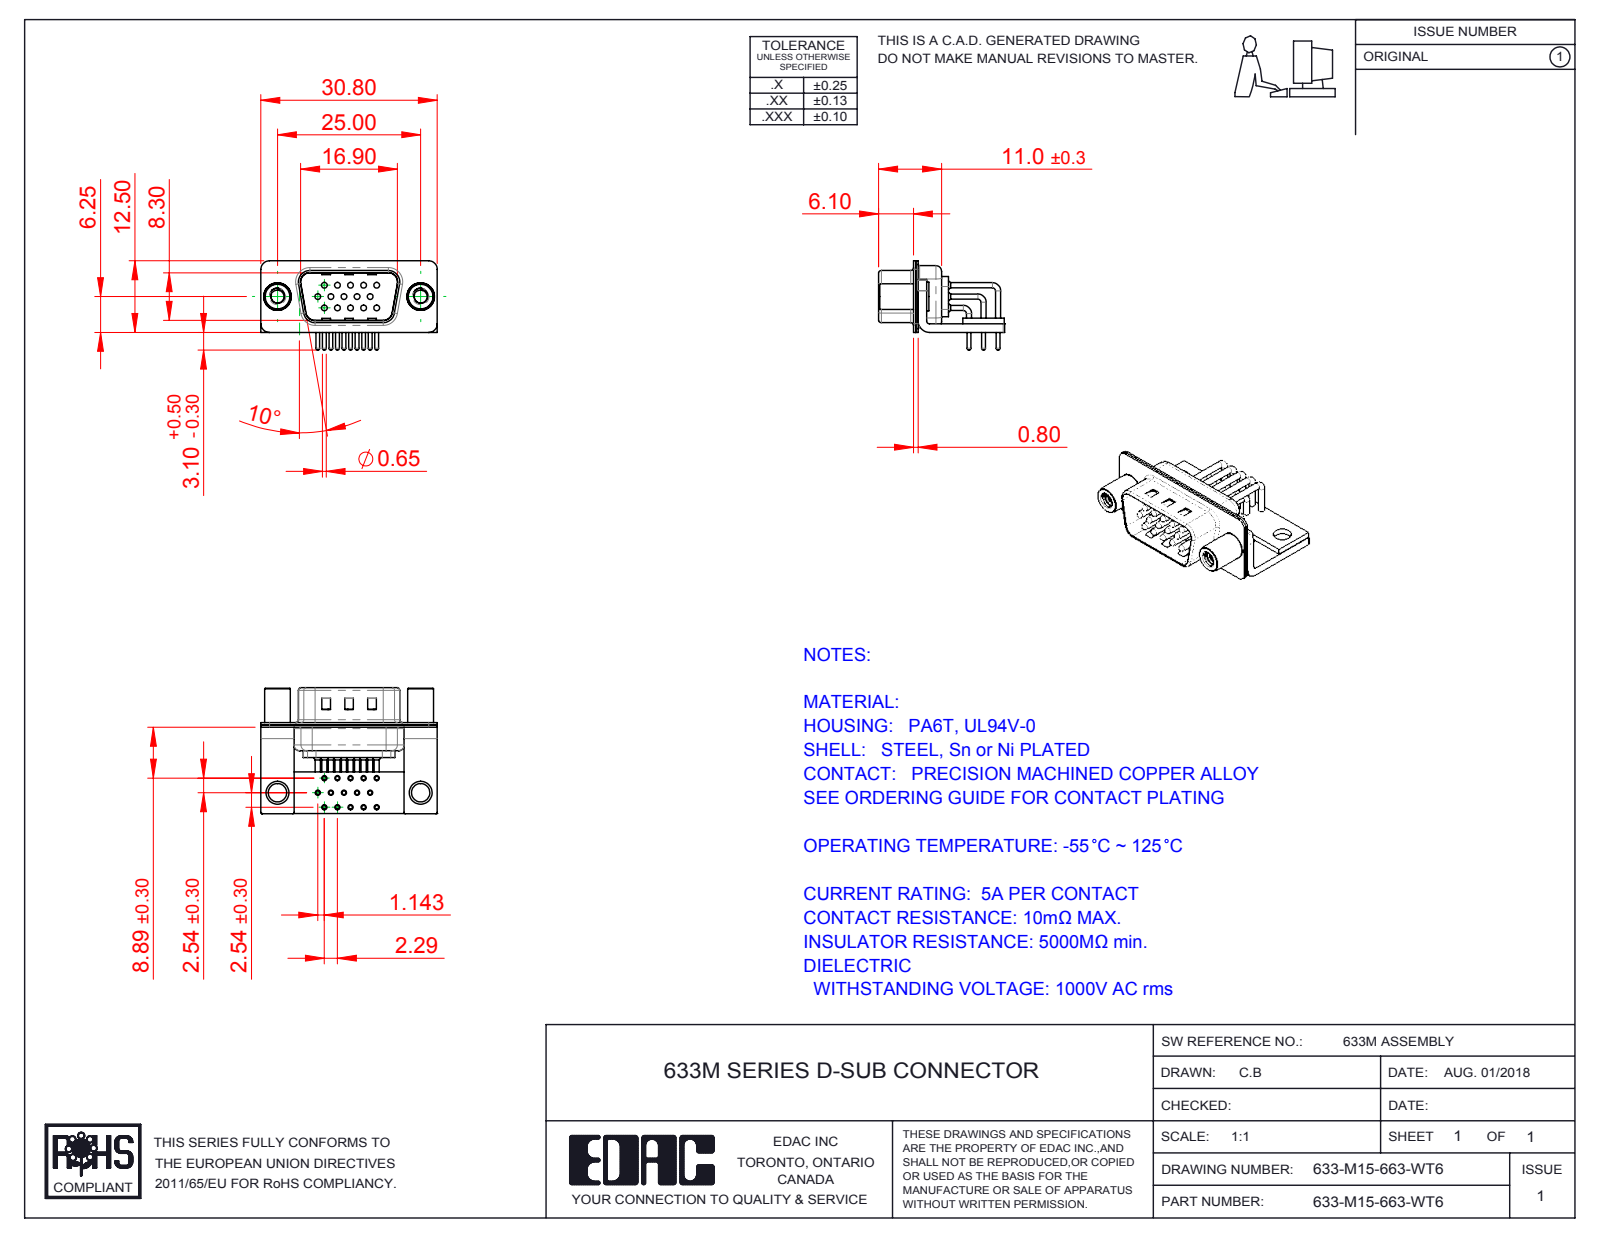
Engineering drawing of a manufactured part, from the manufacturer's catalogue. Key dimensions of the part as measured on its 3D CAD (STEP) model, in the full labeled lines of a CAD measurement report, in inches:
Part name (STEP PRODUCT): 633M Shell Front_15 Contacts; 633M Housing_15 Contacts; 633M Contact Row 1; 633-M15-663-WT6 (+6 more)
STEP written by: SolidWorks 2016 (CONFIG_CONTROL_DESIGN)
Units: inches
Bodies: 23 solids, 2084 faces (1095 planar, 763 cylindrical, 226 other)
Overall size (bounding box): 1.213 × 0.866 × 0.614
Volume: 0.125 in³ · Surface area: 9.444 in²
Round holes (diameter × count): ⌀0.035 ×15, ⌀0.039 ×15, ⌀0.067 ×15, ⌀0.079 ×15, ⌀0.089 ×2, ⌀0.126 ×2, ⌀0.157 ×2, ⌀0.189 ×2
Round bosses / shafts (diameter × count): ⌀0.035 ×16, ⌀0.059 ×15, ⌀0.026 ×15, ⌀0.197 ×2, ⌀0.193 ×2, ⌀0.177 ×2
Partial cylindrical surfaces — rounded edges, fillets, slot ends (radius × count): R0.01 ×16, R0.059 ×16, R0.04 ×15, R0.079 ×13, R0.02 ×9, R0.063 ×8, R0.024 ×4, R0.026 ×4
Main face-to-face distances: 0.016, 0.059, 0.031, 0.039, 0.033, 0.075, 0.049, 0.098, 0.409, 0.376
Hole centre spacings: 0.09, 0.18, 0.09, 0.156, 0.109, 0.168, 0.238, 0.27
